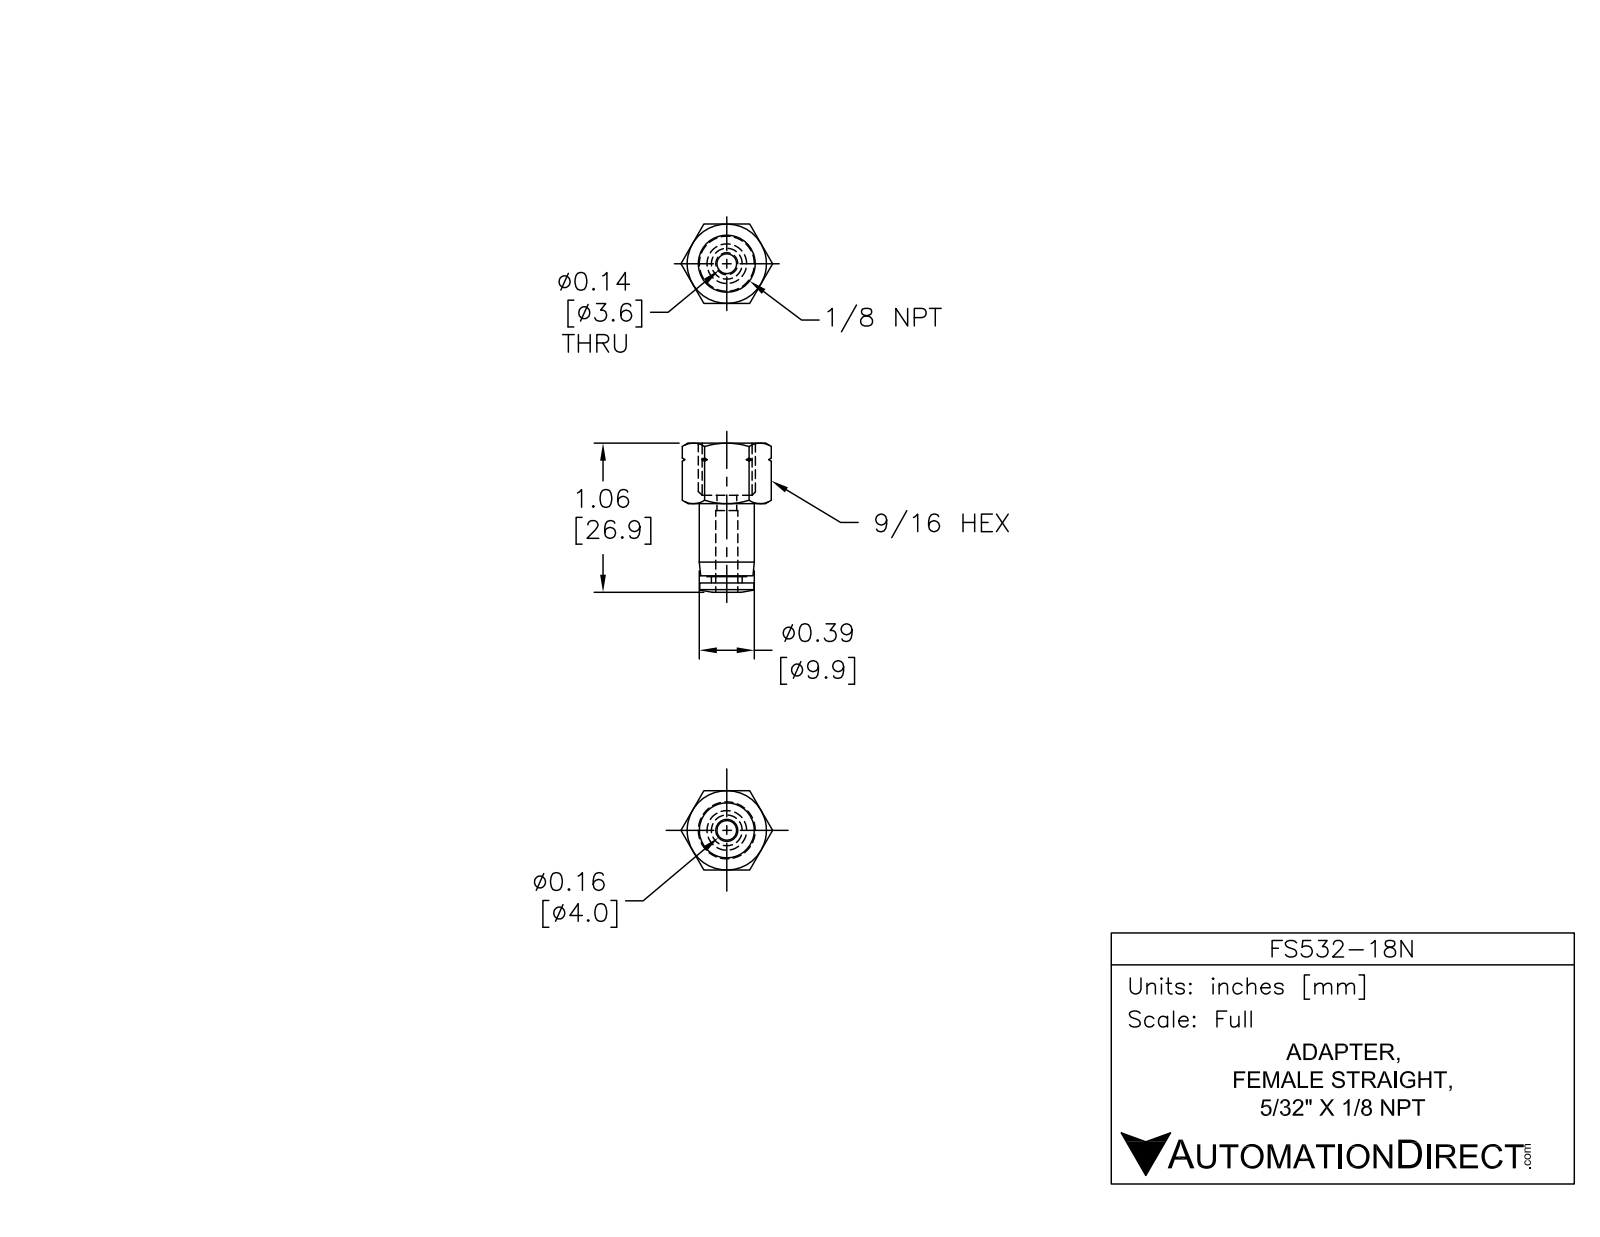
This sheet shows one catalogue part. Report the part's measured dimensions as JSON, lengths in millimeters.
{"part_name": "FS532-18N", "step_written_by": "SolidWorks 2015 (AUTOMOTIVE_DESIGN)", "units": "millimeters", "bodies": {"solids": 1, "faces": 65, "planar": 13, "cylindrical": 12, "other": 40}, "overall_size": [27.1, 16.2, 14], "volume_mm3": 2050, "surface_area_mm2": 1927, "round_holes": [[3.5, 1], [4.3, 1]], "round_bosses_or_shafts": [[10, 1], [9.9, 1], [7.2, 1], [5.6, 1]], "face_to_face_distances": [14, 11, 9.5, 1.5, 25.4, 15.9, 14.4, 1.3, 13.1, 24.1]}
